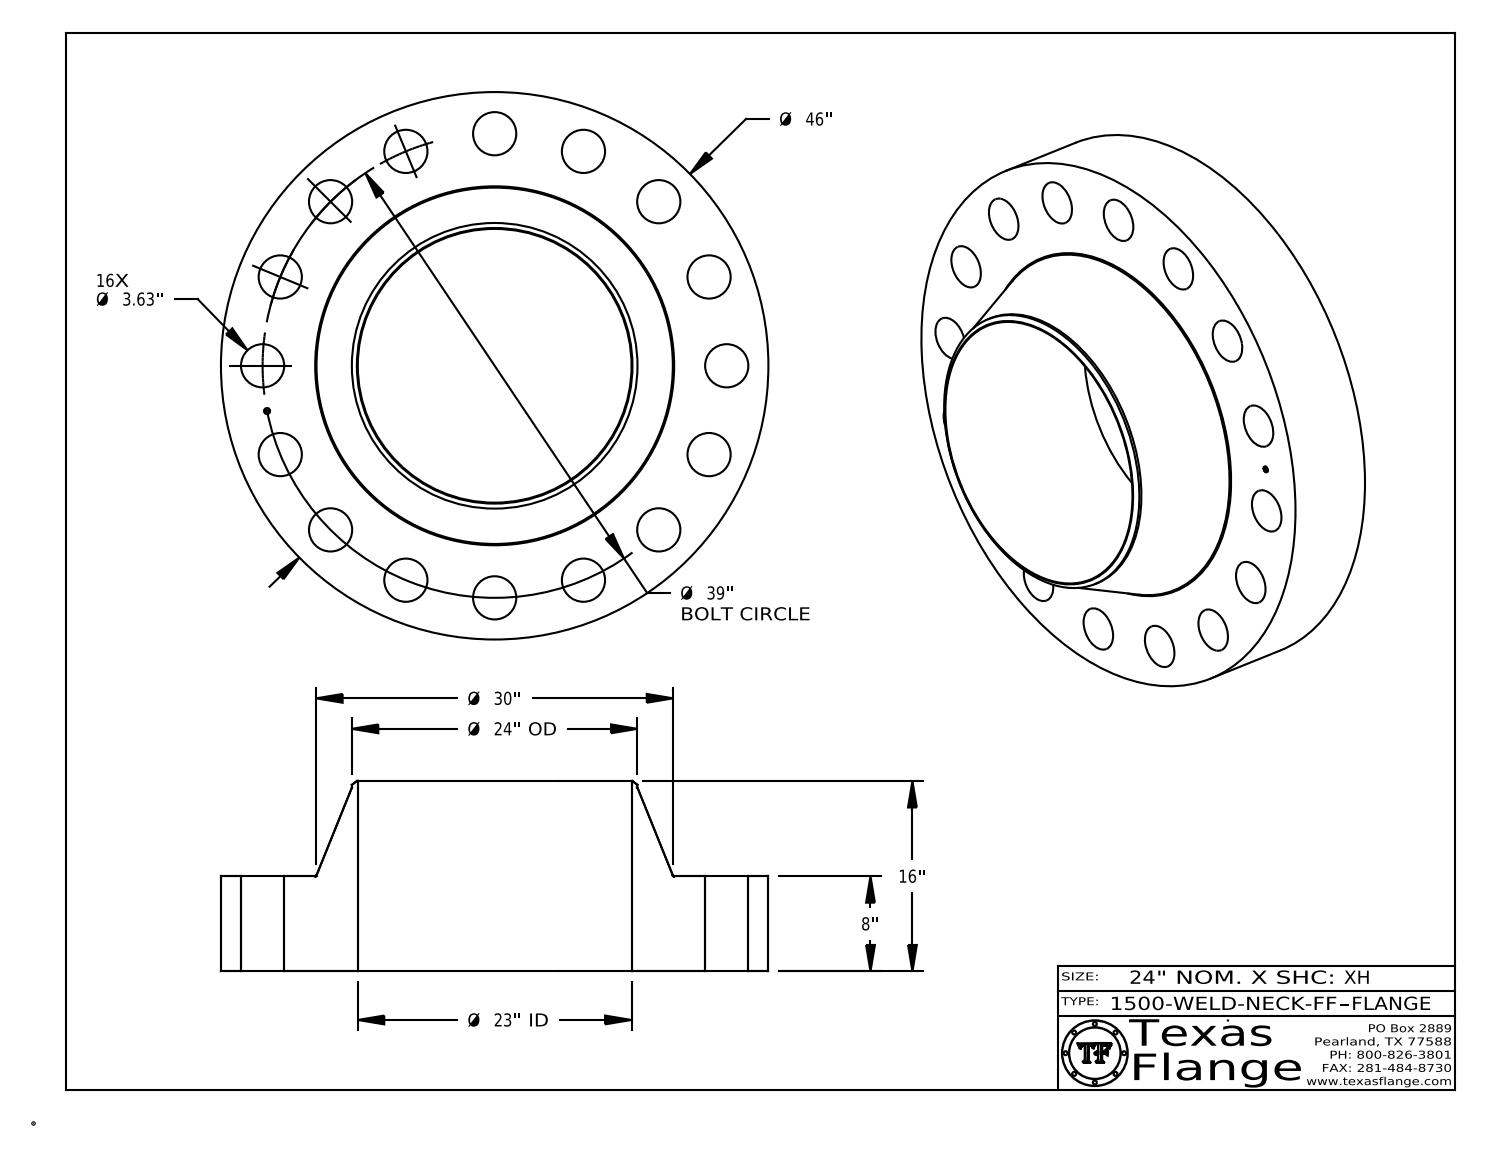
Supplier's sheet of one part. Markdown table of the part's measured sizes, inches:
| quantity | value |
| --- | --- |
| part name | 1500-WELD-NECK-FF |
| STEP written by | CATIA V5 STEP AP214 (AUTOMOTIVE_DESIGN) |
| units | inches |
| bodies | 1 solid, 432 faces (368 planar, 58 cylindrical, 6 other) |
| overall size | 46 × 46 × 16 |
| volume | 9 849 in³ |
| surface area | 6 384 in² |
| round holes (diameter × count) | 3.63 × 16, 0.495 × 1, 23 × 1 |
| round bosses / shafts (diameter × count) | 0.03 × 8, 46 × 1, 24 × 1, 0.39 × 1 |
| main face-to-face distances | 8, 16, 7.985, 0.015, 8.015, 0.148, 0.145, 0.027, 0.096, 0.123 |
| hole center spacings | 19.5, 21.667, 27.577, 38.251, 14.925, 36.031, 7.608, 7.609 |
